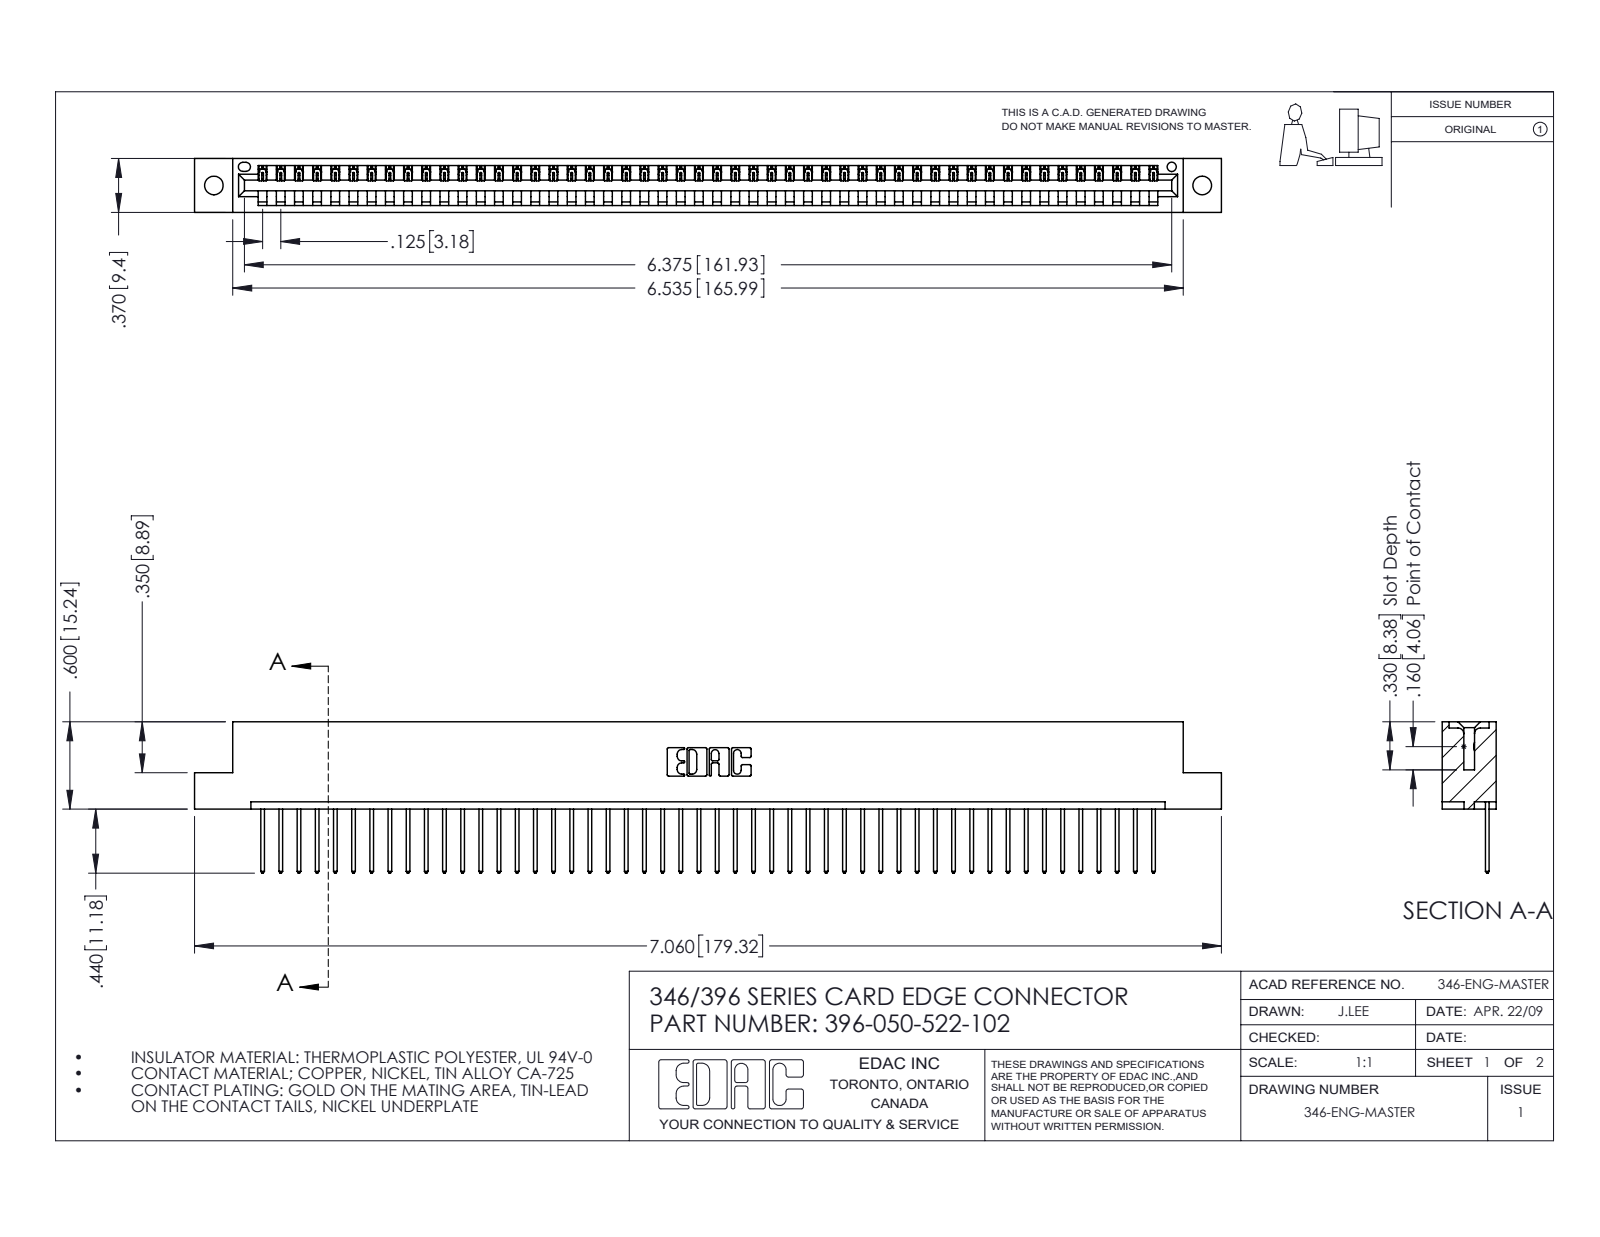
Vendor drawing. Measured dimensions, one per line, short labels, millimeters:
name: 396-050-522-102; 345-292-001_345-293-122; 346 Part_Flush Mounting Lugs - 0.128 Dia
written by: SolidWorks 2016 (CONFIG_CONTROL_DESIGN)
unit: mm
bodies: 51 solids, 3022 faces (2076 planar, 946 cylindrical, 0 other)
size: 179.3 × 26.4 × 9.4
volume: 17 190 mm³; area: 21 480 mm²
holes: 2× ⌀3.3, 1× ⌀1.6
rounds: 100× R0.2, 100× R0.3, 22× R0.3, 6× R0.2, 6× R0.8, 3× R0.7, 2× R0.8, 2× R1
face distances: 1.2, 8.2, 9.4, 6.4, 1.8, 7.6, 0.6, 3.8, 5.6, 2.5
hole spacings: 6.2, 167.3, 172.6
